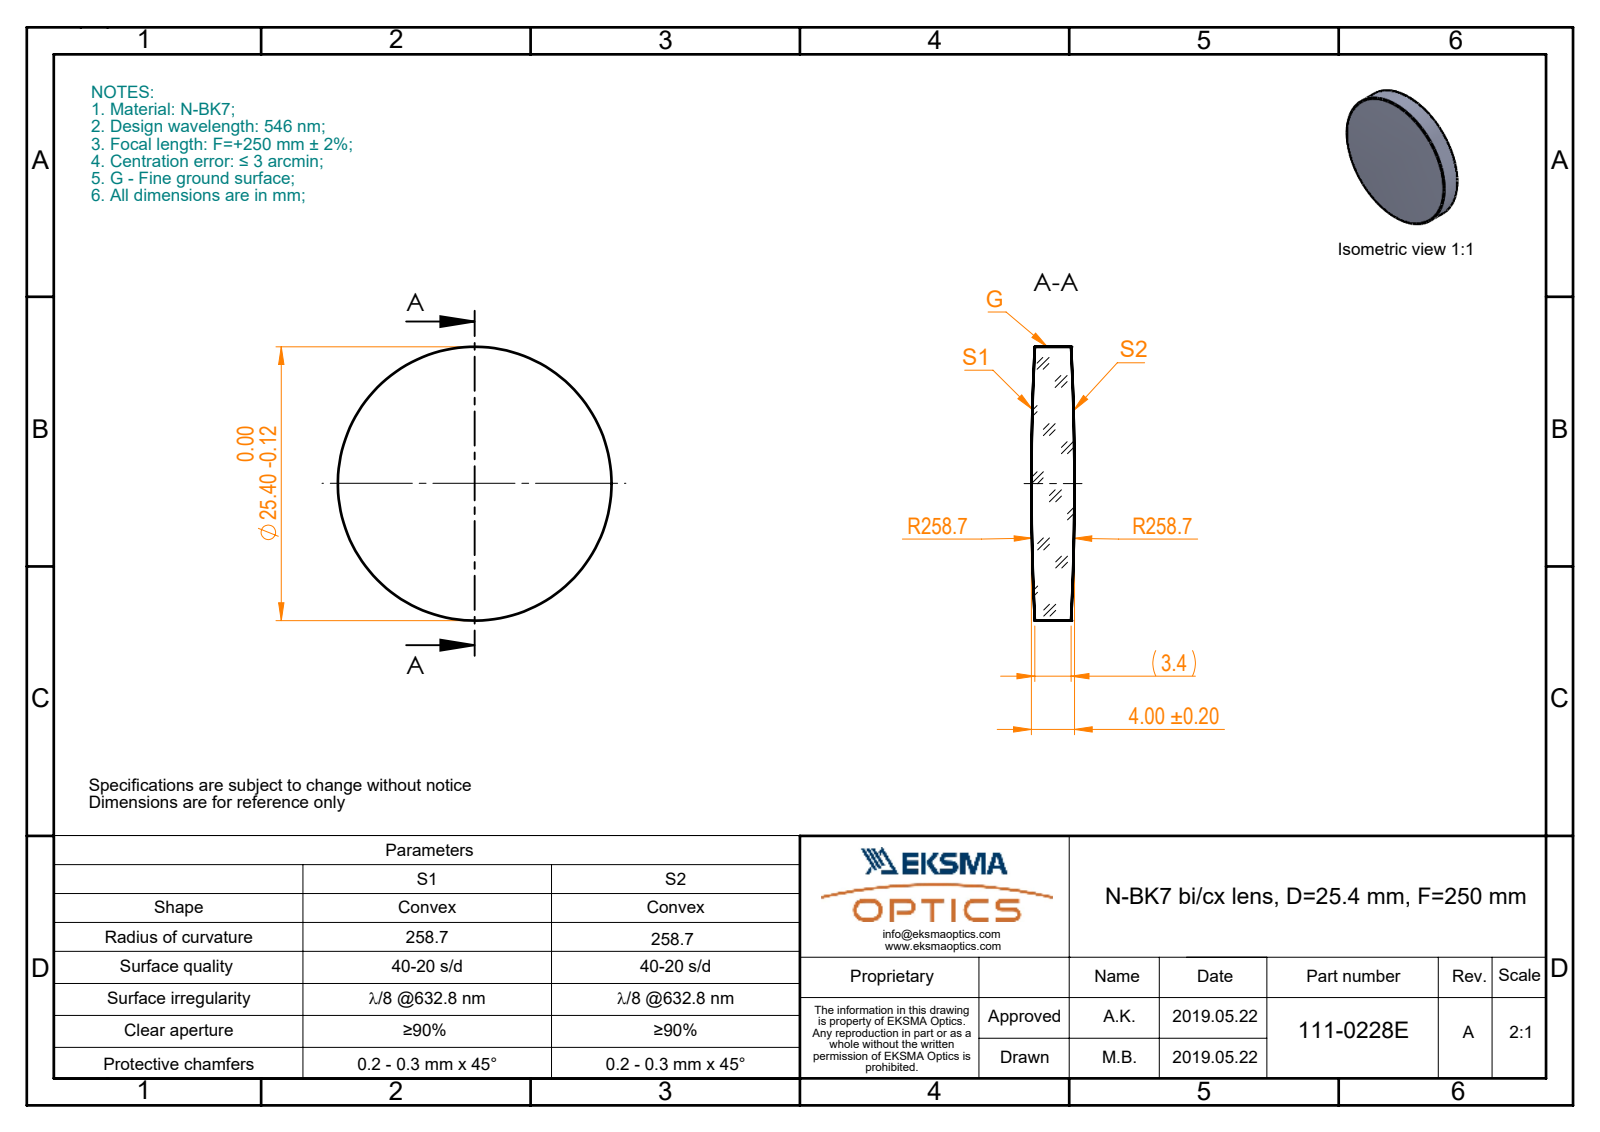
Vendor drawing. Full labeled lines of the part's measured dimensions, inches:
Part name (STEP PRODUCT): 111-0228E BK7 bi-cx 25.4 F250
STEP written by: SolidWorks 2017 (CONFIG_CONTROL_DESIGN)
Units: inches
Bodies: 1 solid, 6 faces (0 planar, 2 cylindrical, 4 other)
Overall size (bounding box): 1 × 1 × 0.157
Volume: 0.114 in³ · Surface area: 1.989 in²
Round bosses / shafts (diameter × count): ⌀1 ×1
